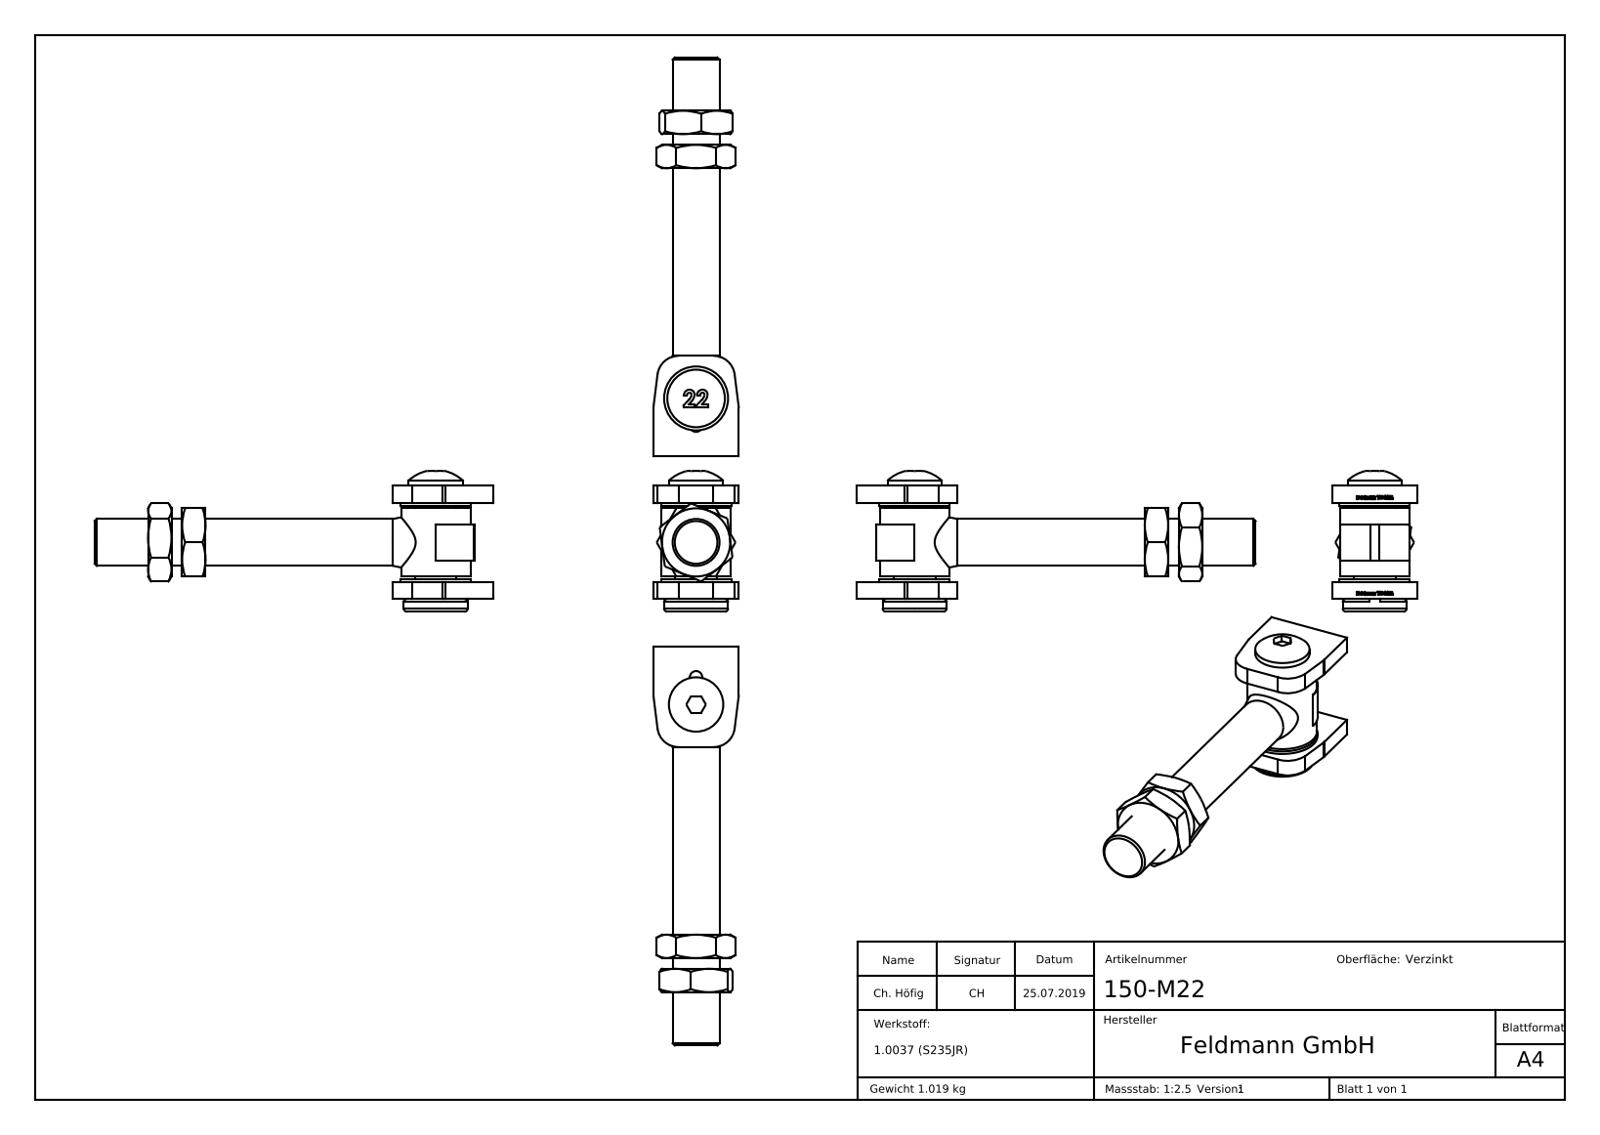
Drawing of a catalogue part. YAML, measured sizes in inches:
part_name: "150-MXX Teil3_150-M22 Teil3; 150-MXX Teil1_150-M22 Teil1; 150-MXX Teil5_150-M22 Teil5; 150-MXX Teil2_150-M22 Teil2 (+3 more)"
step_written_by: "SolidWorks 2018 (CONFIG_CONTROL_DESIGN)"
units: inches
bodies: {solids: 9, faces: 538, planar: 305, cylindrical: 30, other: 203}
overall_size: [7.362, 2.601, 1.575]
volume: 8.034
surface_area: 65.17
round_holes:
  - {diameter: 0.335, count: 1}
  - {diameter: 0.472, count: 1}
  - {diameter: 0.768, count: 1}
  - {diameter: 0.787, count: 1}
  - {diameter: 0.795, count: 1}
  - {diameter: 0.866, count: 1}
round_bosses_or_shafts:
  - {diameter: 1.299, count: 1}
  - {diameter: 1.28, count: 1}
  - {diameter: 1.181, count: 1}
  - {diameter: 1.004, count: 1}
  - {diameter: 0.866, count: 1}
  - {diameter: 0.768, count: 1}
  - {diameter: 0.394, count: 1}
partial_cylinders:
  - {radius: 0.394, count: 5}
  - {radius: 0.709, count: 2}
  - {radius: 0.114, count: 1}
face_to_face_distances: [0.315, 1.772, 1.457, 2.087, 1.26, 0.413, 1.673, 0.098, 1.358, 0.63]
